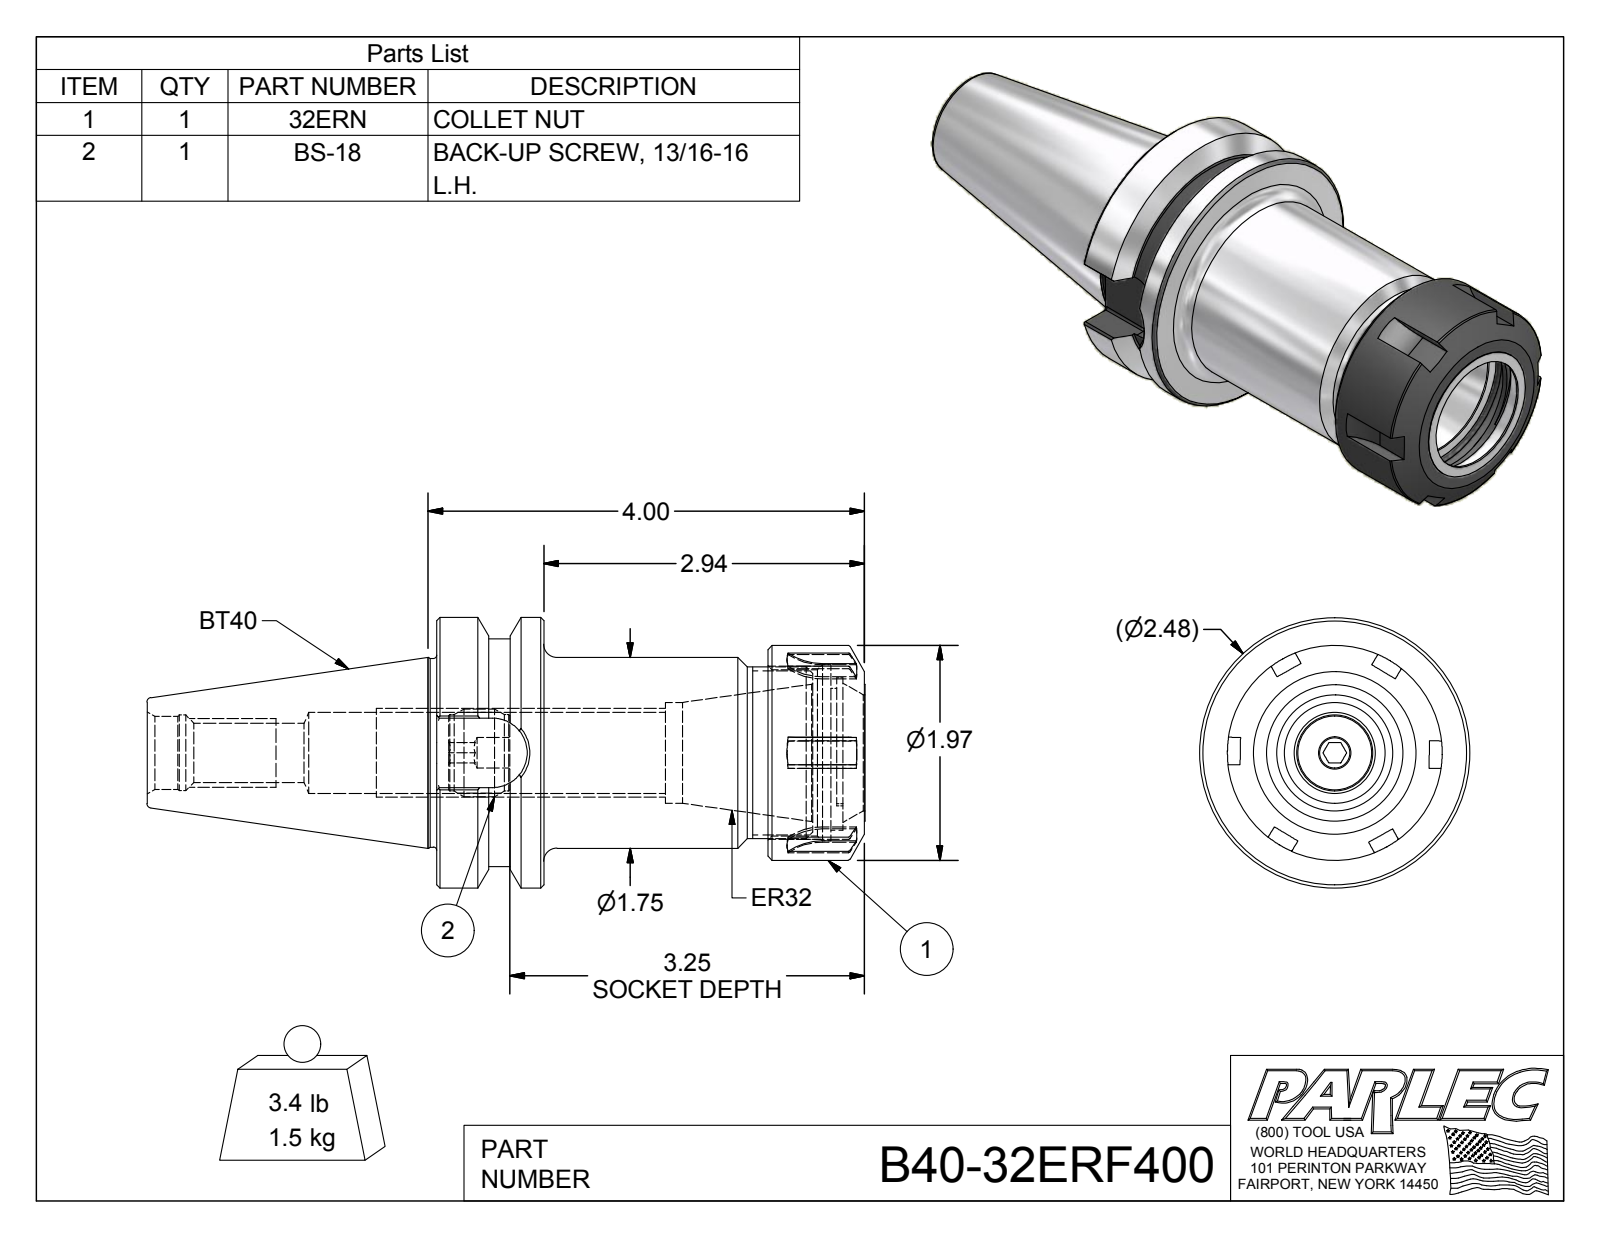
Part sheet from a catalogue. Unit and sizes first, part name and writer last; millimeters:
Units: millimetres
Overall size (bounding box): 167 × 62.99 × 62.99
Round holes (diameter × count): ⌀7.11 ×1, ⌀13.84 ×1, ⌀17.01 ×1, ⌀17.62 ×1, ⌀18.92 ×1, ⌀23.5 ×1, ⌀27 ×1, ⌀33.02 ×1, ⌀38.65 ×1, ⌀41 ×1
Round bosses / shafts (diameter × count): ⌀62.99 ×1, ⌀53.01 ×1, ⌀50 ×1, ⌀44.45 ×1, ⌀43.94 ×1, ⌀40 ×1, ⌀20.45 ×1, ⌀17.78 ×1
Partial cylindrical surfaces — rounded edges, fillets, slot ends (radius × count): R0.51 ×20, R8.09 ×1, R14.9 ×1, R17.5 ×1
Main face-to-face distances: 24.99, 99.62, 74.63, 76.84, 51.85, 22.78, 91.85, 66.86, 15.01, 7.77
Hole centre spacings: 1.85
Volume: 198 260 mm³ · Surface area: 46 018 mm²
Bodies: 3 solids, 173 faces (67 planar, 46 cylindrical, 60 other)
Part name (STEP PRODUCT): B40-32ER4-1; 32ERN; BS-18; B40-32ERF400
STEP written by: Autodesk Inventor 2016 (AUTOMOTIVE_DESIGN)
